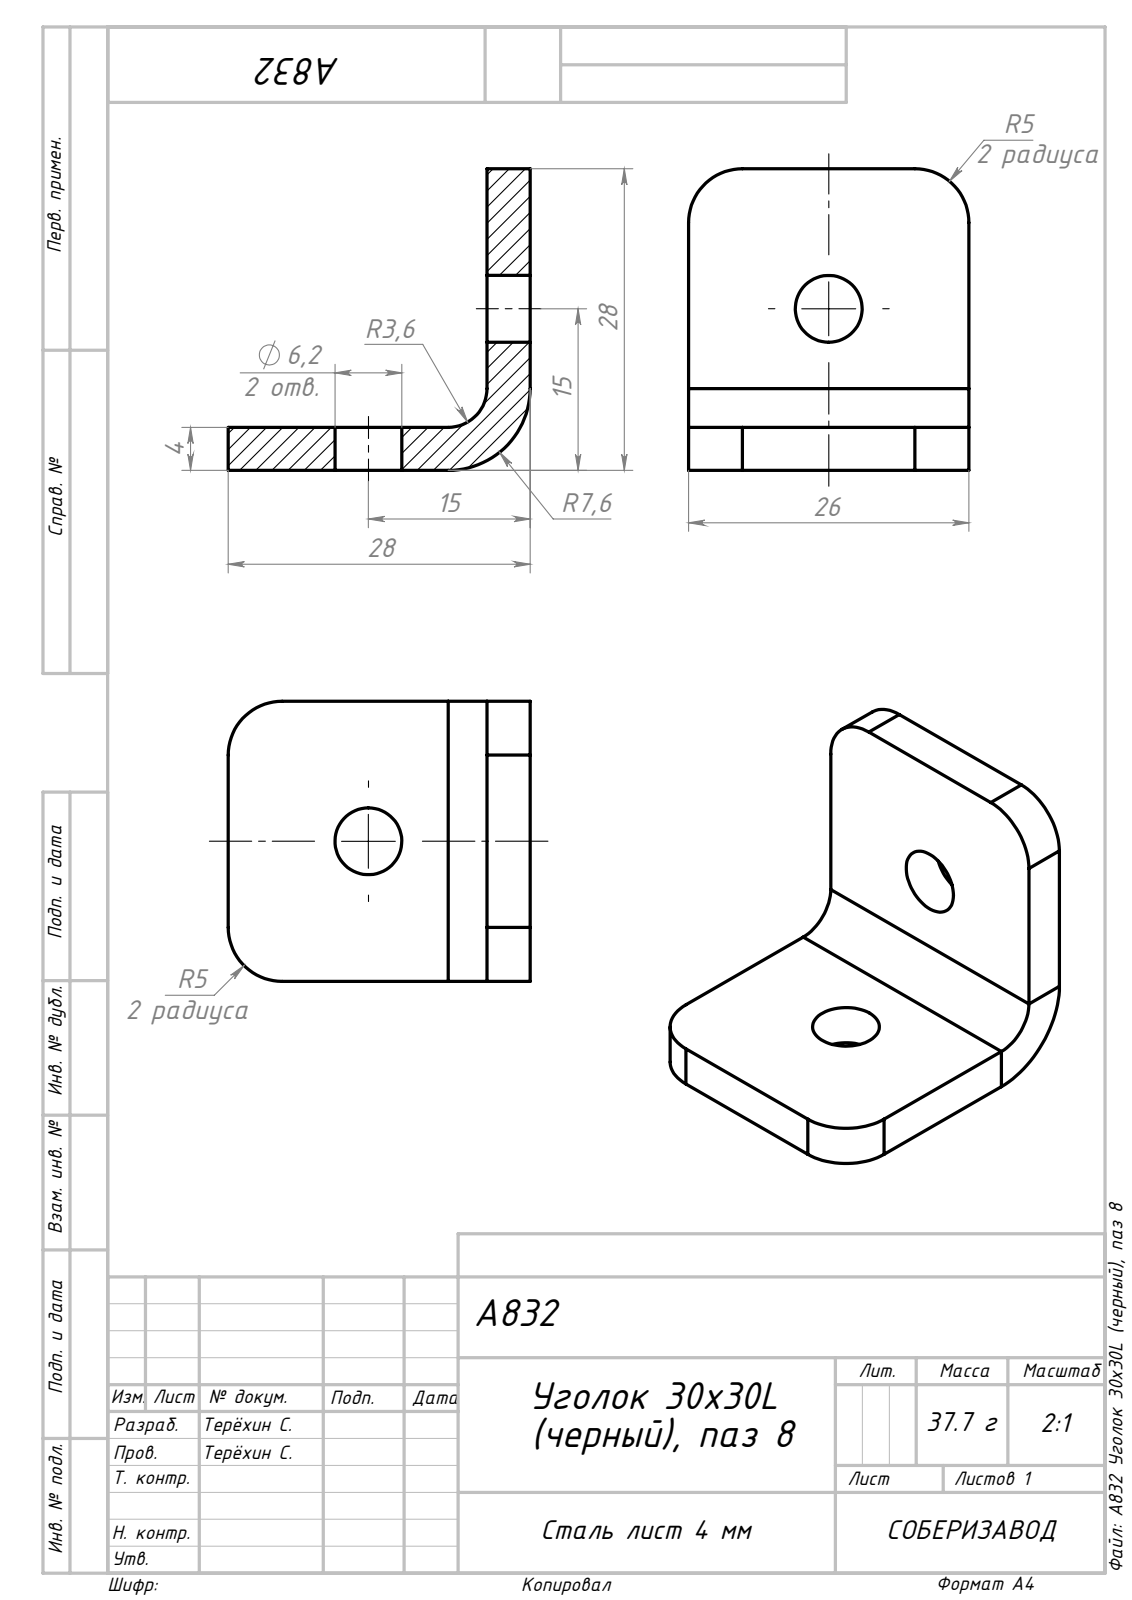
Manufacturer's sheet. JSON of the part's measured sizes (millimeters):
{"part_name": "Сборка1; A832 Уголок 30х30L (черный), паз 8_00", "step_written_by": "SolidWorks 2022 (AUTOMOTIVE_DESIGN)", "units": "millimeters", "bodies": {"solids": 1, "faces": 22, "planar": 12, "cylindrical": 10, "other": 0}, "overall_size": [28, 28, 26], "volume_mm3": 4831, "surface_area_mm2": 3142, "round_holes": [[6.2, 2]], "partial_cylinders_radius": [[5, 4], [3.6, 1], [7.6, 1]], "face_to_face_distances": [4, 26, 28, 24]}
